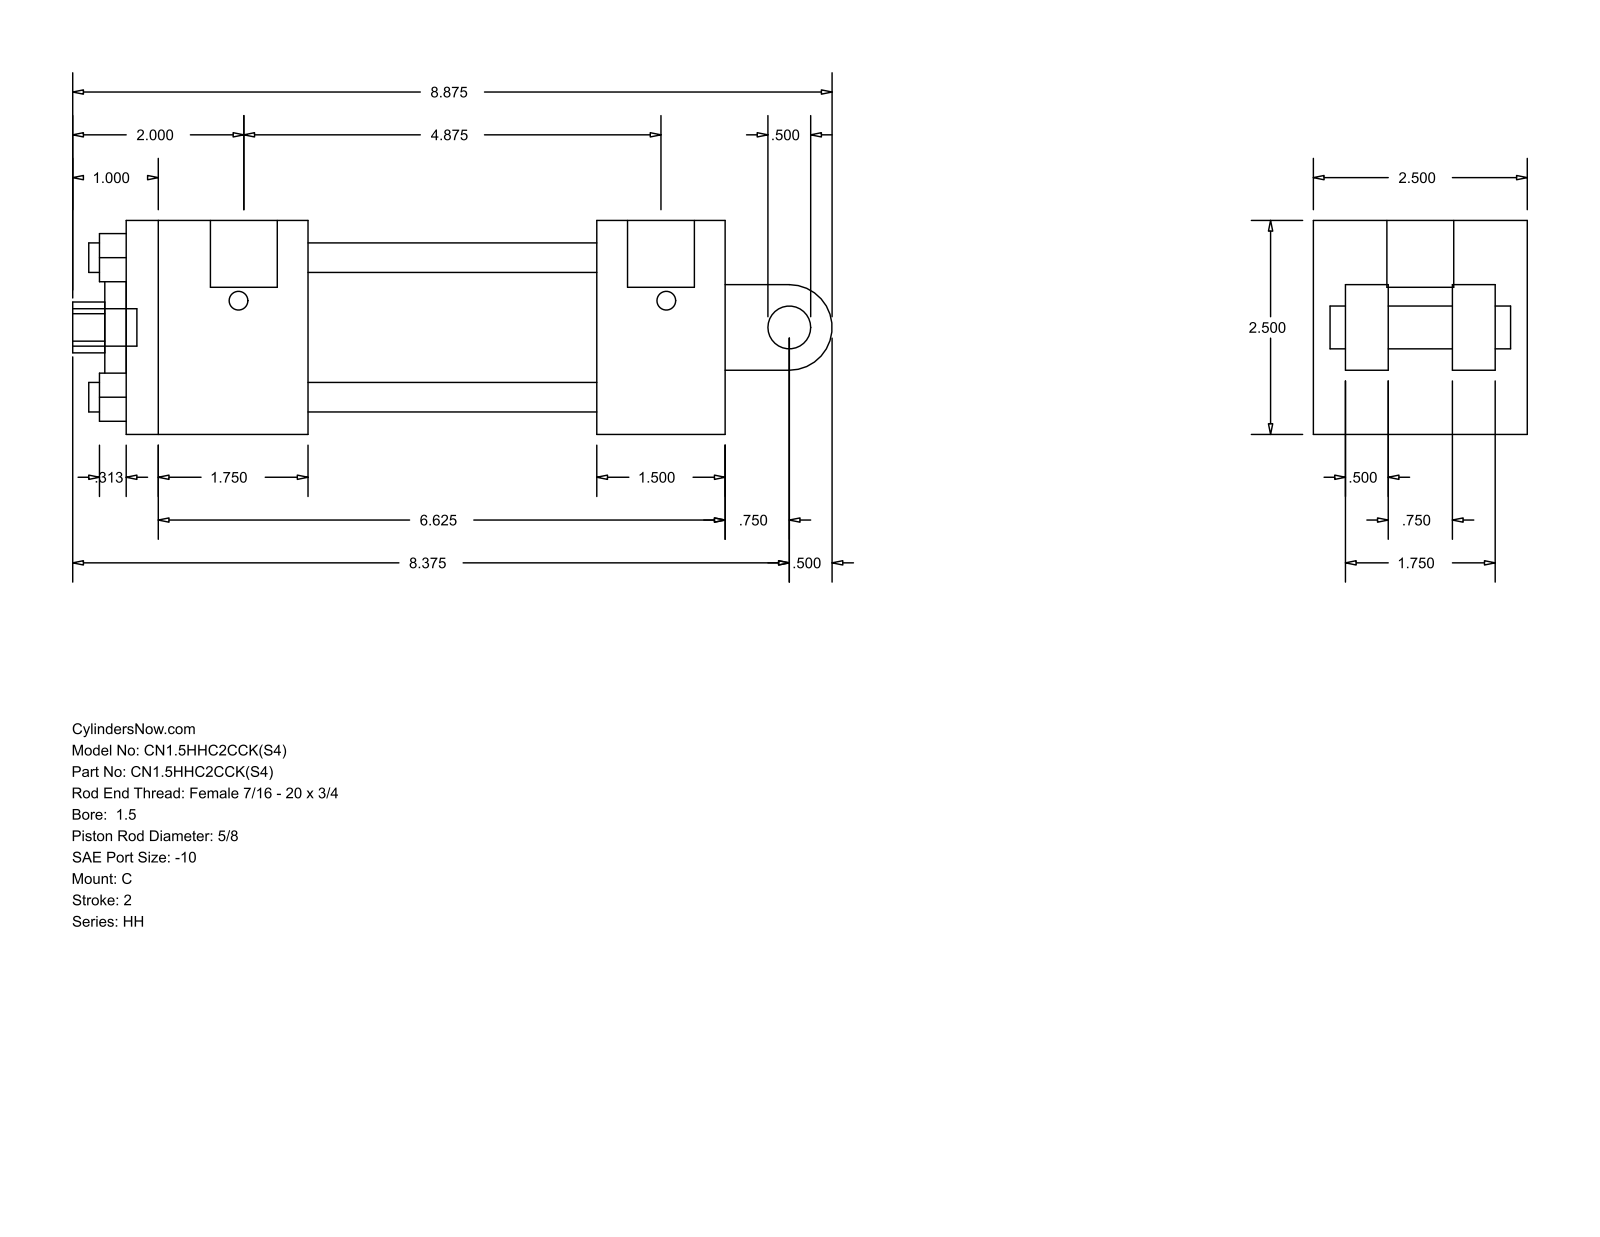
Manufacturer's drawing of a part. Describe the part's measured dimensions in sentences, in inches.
The part is named "HH_C__0150_0.625". Its 3-D file was written by "GSSL Pune (CONFIG_CONTROL_DESIGN)". It is 0 solids with 99 faces: 70 planar, 29 cylindrical and 0 other. Overall it measures 8.875 by 2.5 by 2.5 inches. Round holes: 4 of diameter 0.345, 2 of diameter 0.219, 1 of diameter 0.625, 1 of diameter 0.781, 1 of diameter 1.125, 1 of diameter 1.75. Round bosses or shafts: 2 of diameter 0.219, 1 of diameter 0.781, 1 of diameter 0.5, 1 of diameter 0.437. Partial cylindrical surfaces (rounded edges, fillets, slot ends): 1 of radius 0.297, 1 of radius 0.5. The main face-to-face distances are 2.5, 7, 2.125, 5.5, 3.375, 4.875, 1.5, 0.5, 0.375, 0.75. The hole center spacings are 1.152, 1.63, 2.305, 0.063.
